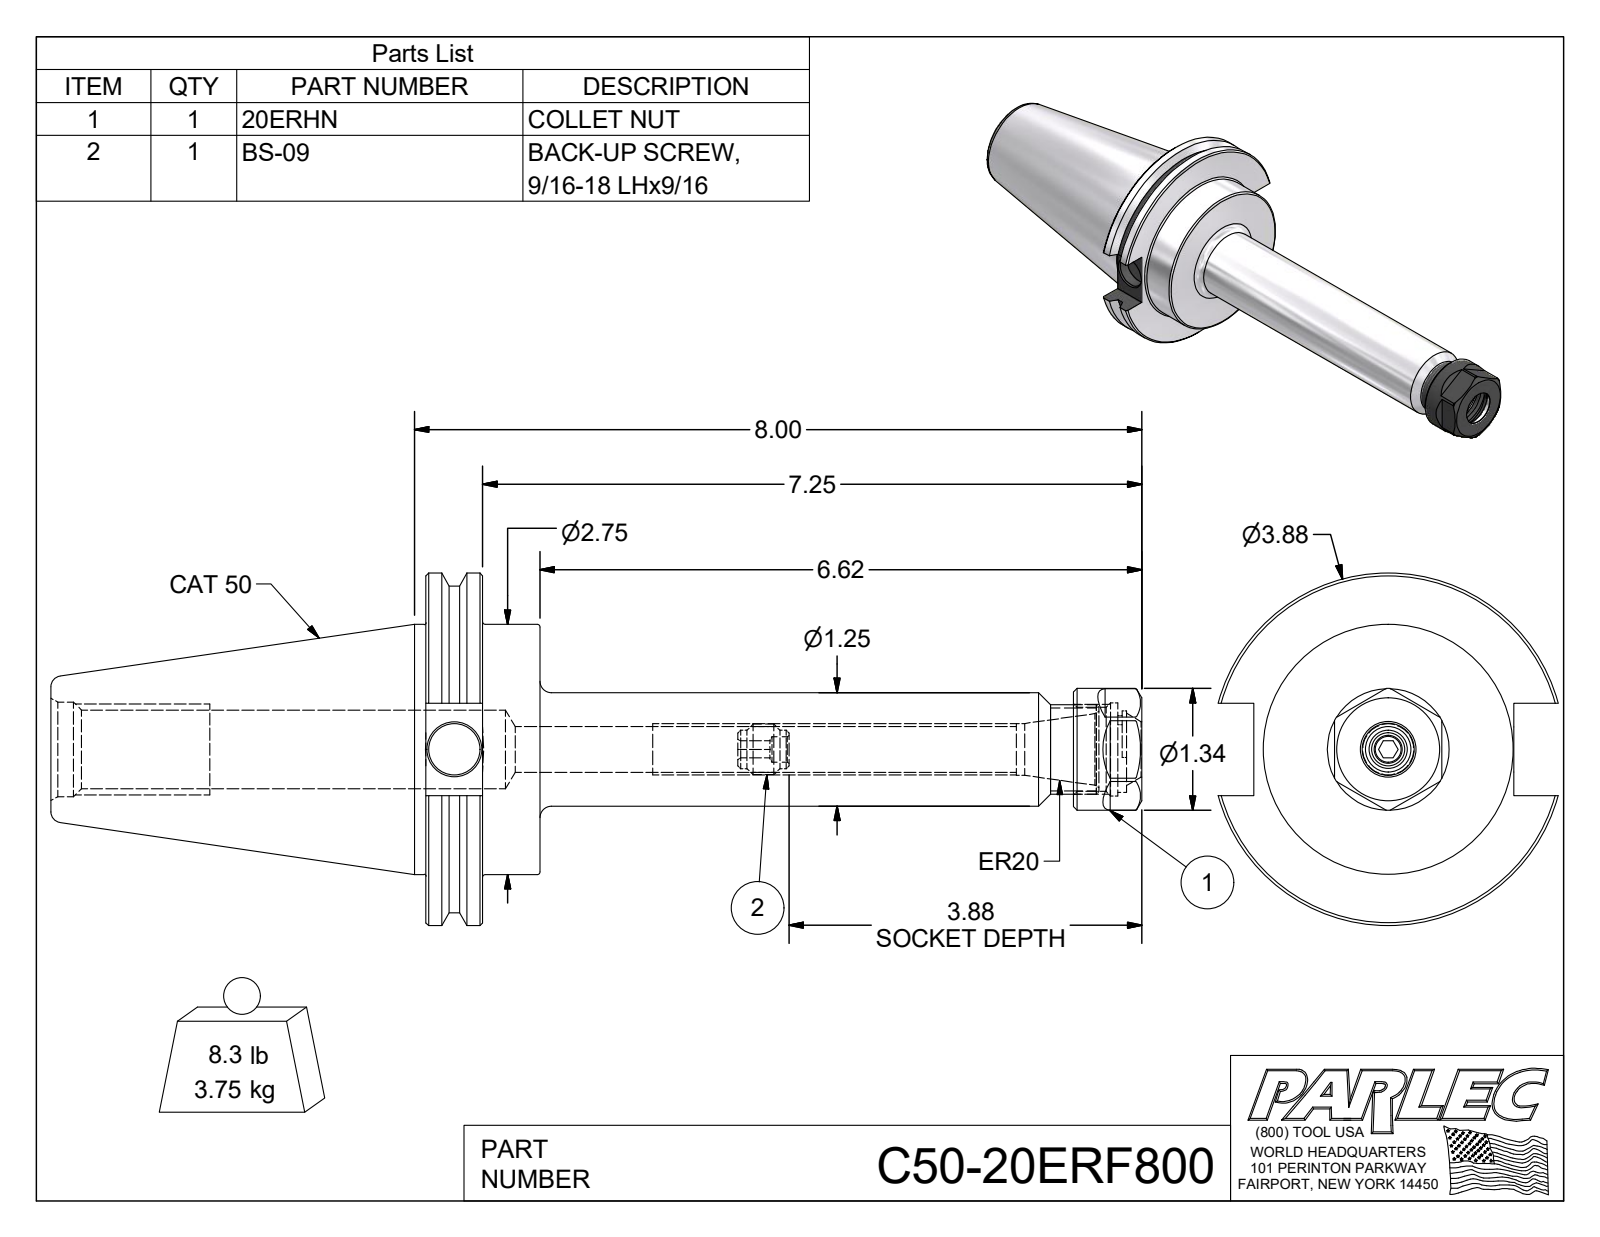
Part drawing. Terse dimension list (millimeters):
name: C50-20ER8-1; 20ERHN; BS-09; C50-20ERF800
written by: Autodesk Inventor 2016 (AUTOMOTIVE_DESIGN)
unit: mm
bodies: 3 solids, 109 faces (43 planar, 26 cylindrical, 40 other)
size: 304.8 × 98.42 × 94.99
volume: 481 456 mm³; area: 75 183 mm²
holes: 1× ⌀7.14, 1× ⌀12.75, 1× ⌀14.3, 1× ⌀14.48, 1× ⌀15.49, 1× ⌀21.97, 1× ⌀23.5, 1× ⌀26, 1× ⌀26.37
bosses: 1× ⌀98.42, 1× ⌀91.29, 1× ⌀69.85, 1× ⌀34, 1× ⌀31.75, 1× ⌀25, 1× ⌀14.1, 1× ⌀10.72
rounds: 1× R9.47, 1× R10.55, 1× R10.75
face distances: 15.88, 31.88, 16, 200.03, 184.15, 168.15, 30, 104.77, 120.65, 136.65
